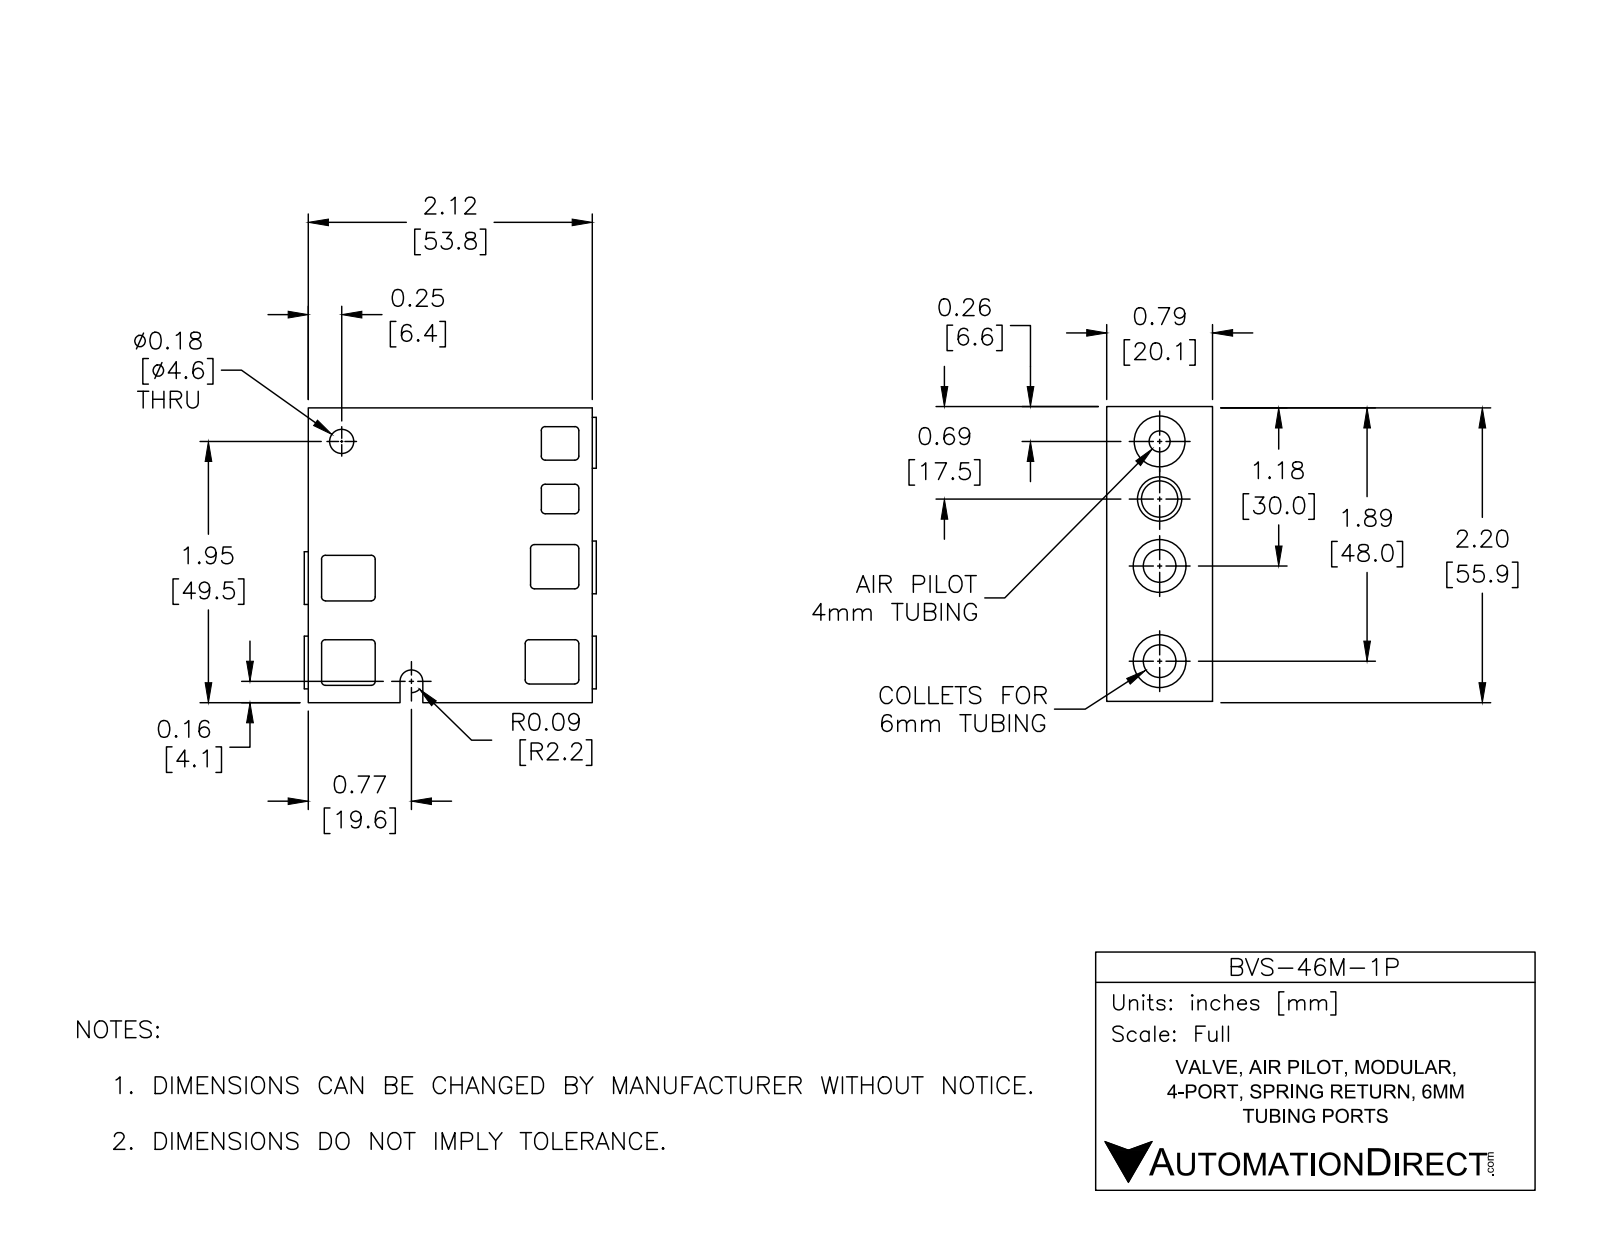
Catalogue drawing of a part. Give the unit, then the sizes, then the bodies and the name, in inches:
Units: inches
Overall size (bounding box): 2.2 × 2.18 × 0.79
Round holes (diameter × count): ⌀0.244 ×3, ⌀0.06 ×1, ⌀0.161 ×1, ⌀0.18 ×1
Round bosses / shafts (diameter × count): ⌀0.394 ×3, ⌀0.38 ×1, ⌀0.27 ×1
Partial cylindrical surfaces — rounded edges, fillets, slot ends (radius × count): R0.03 ×24, R0.085 ×1
Main face-to-face distances: 0.79, 0.1, 2.2, 2.12, 0.69, 0.59, 0.03, 2.15, 0.13, 2.02
Hole centre spacings: 0.08, 0.63, 0.71, 0.93, 1.01, 1.64
Volume: 3.372 in³ · Surface area: 21.14 in²
Bodies: 1 solid, 158 faces (81 planar, 75 cylindrical, 2 other)
Part name (STEP PRODUCT): BVS-46M-1P
STEP written by: SolidWorks 2016 (AUTOMOTIVE_DESIGN)
